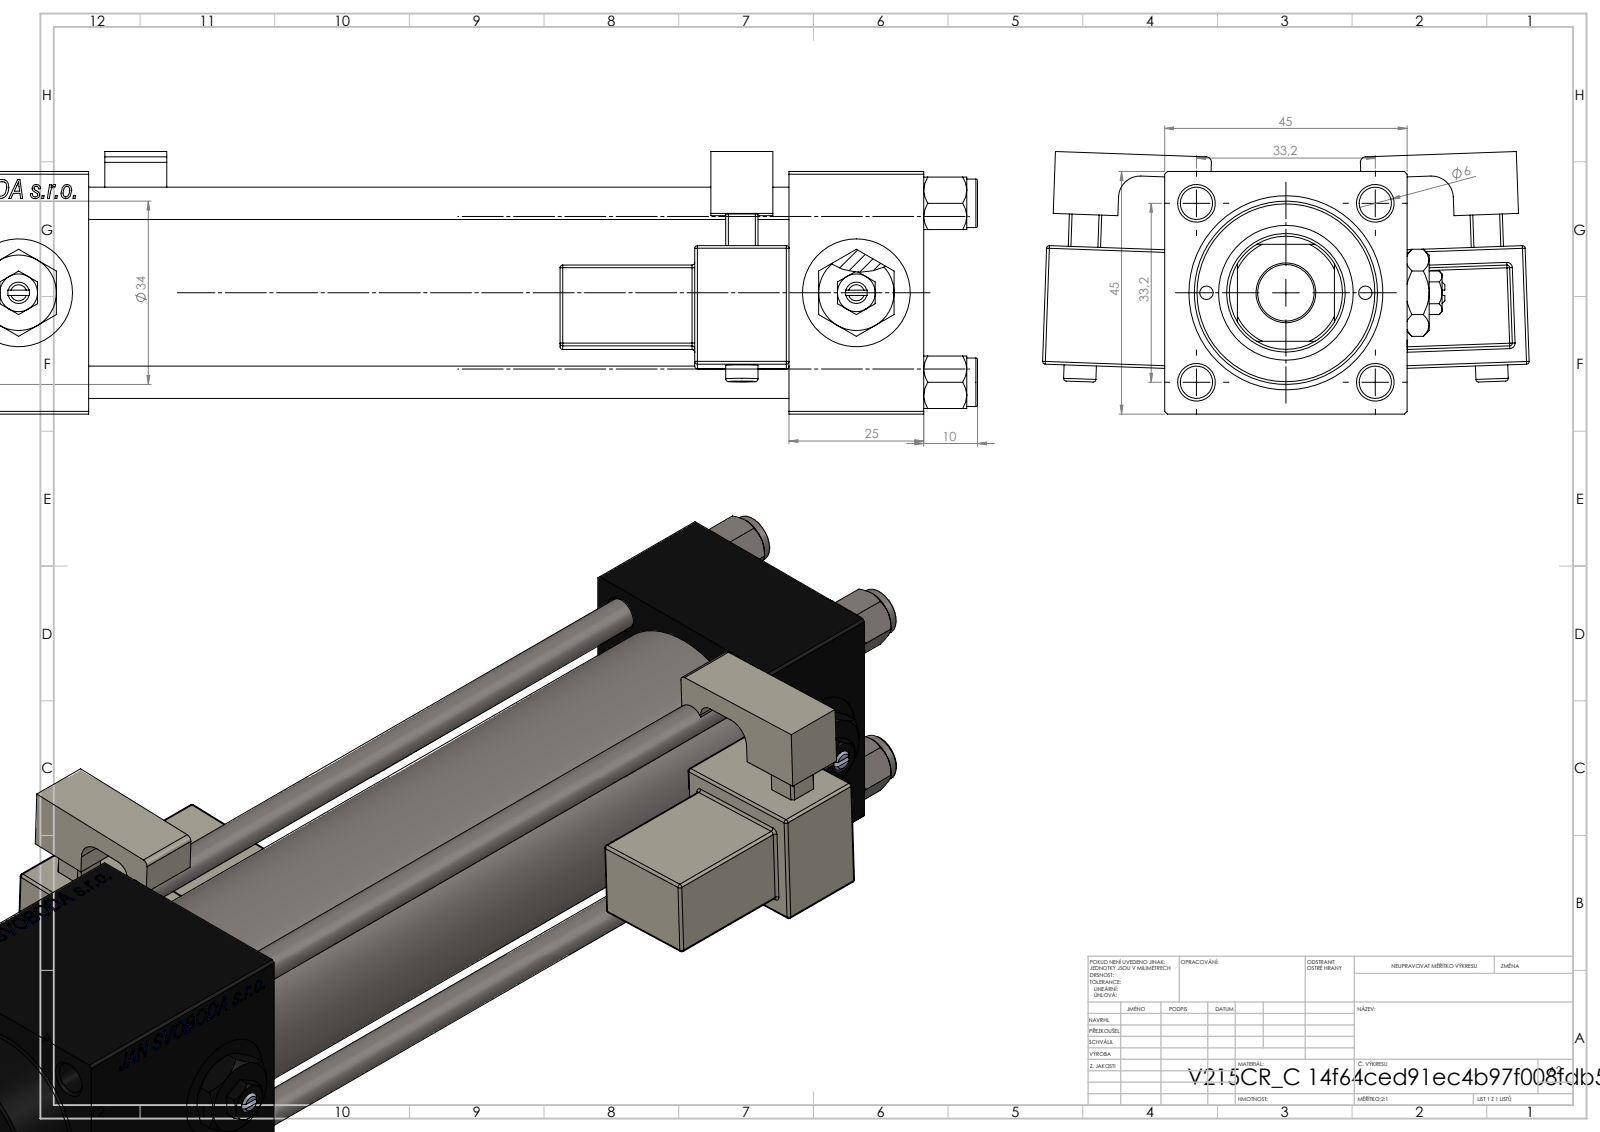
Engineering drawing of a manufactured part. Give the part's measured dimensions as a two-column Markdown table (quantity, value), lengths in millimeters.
| quantity | value |
| --- | --- |
| part name | MFA; Zatka_pro_OIL_PORT; V215CR_C_TYCINKA; V215CR_C_Body (+5 more) |
| STEP written by | SolidWorks 2019 (CONFIG_CONTROL_DESIGN) |
| units | millimeters |
| bodies | 17 solids, 1497 faces (664 planar, 175 cylindrical, 658 other) |
| overall size | 299 × 90.31 × 48.72 |
| volume | 332 524 mm³ |
| surface area | 121 686 mm² |
| round holes (diameter × count) | 6 × 4, 2.5 × 2, 7 × 2, 13.16 × 2, 20 × 2, 10.5 × 1, 22 × 1, 24 × 1, 25 × 1, 32 × 1, 33 × 1 |
| round bosses / shafts (diameter × count) | 9 × 4, 6 × 2, 38 × 1, 34 × 1, 28 × 1, 18 × 1, 12 × 1, 11 × 1 |
| partial cylindrical surfaces (radius × count) | 0.5 × 48, 1 × 2, 2.5 × 2, 4 × 2, 9.75 × 1, 10.5 × 1 |
| main face-to-face distances | 45, 25, 3, 155, 130, 203, 22.99, 44.8, 14.5, 13 |
| hole center spacings | 16.7, 23.48, 33.2, 35.47, 14.75, 46.95, 29.5, 155.5 |
